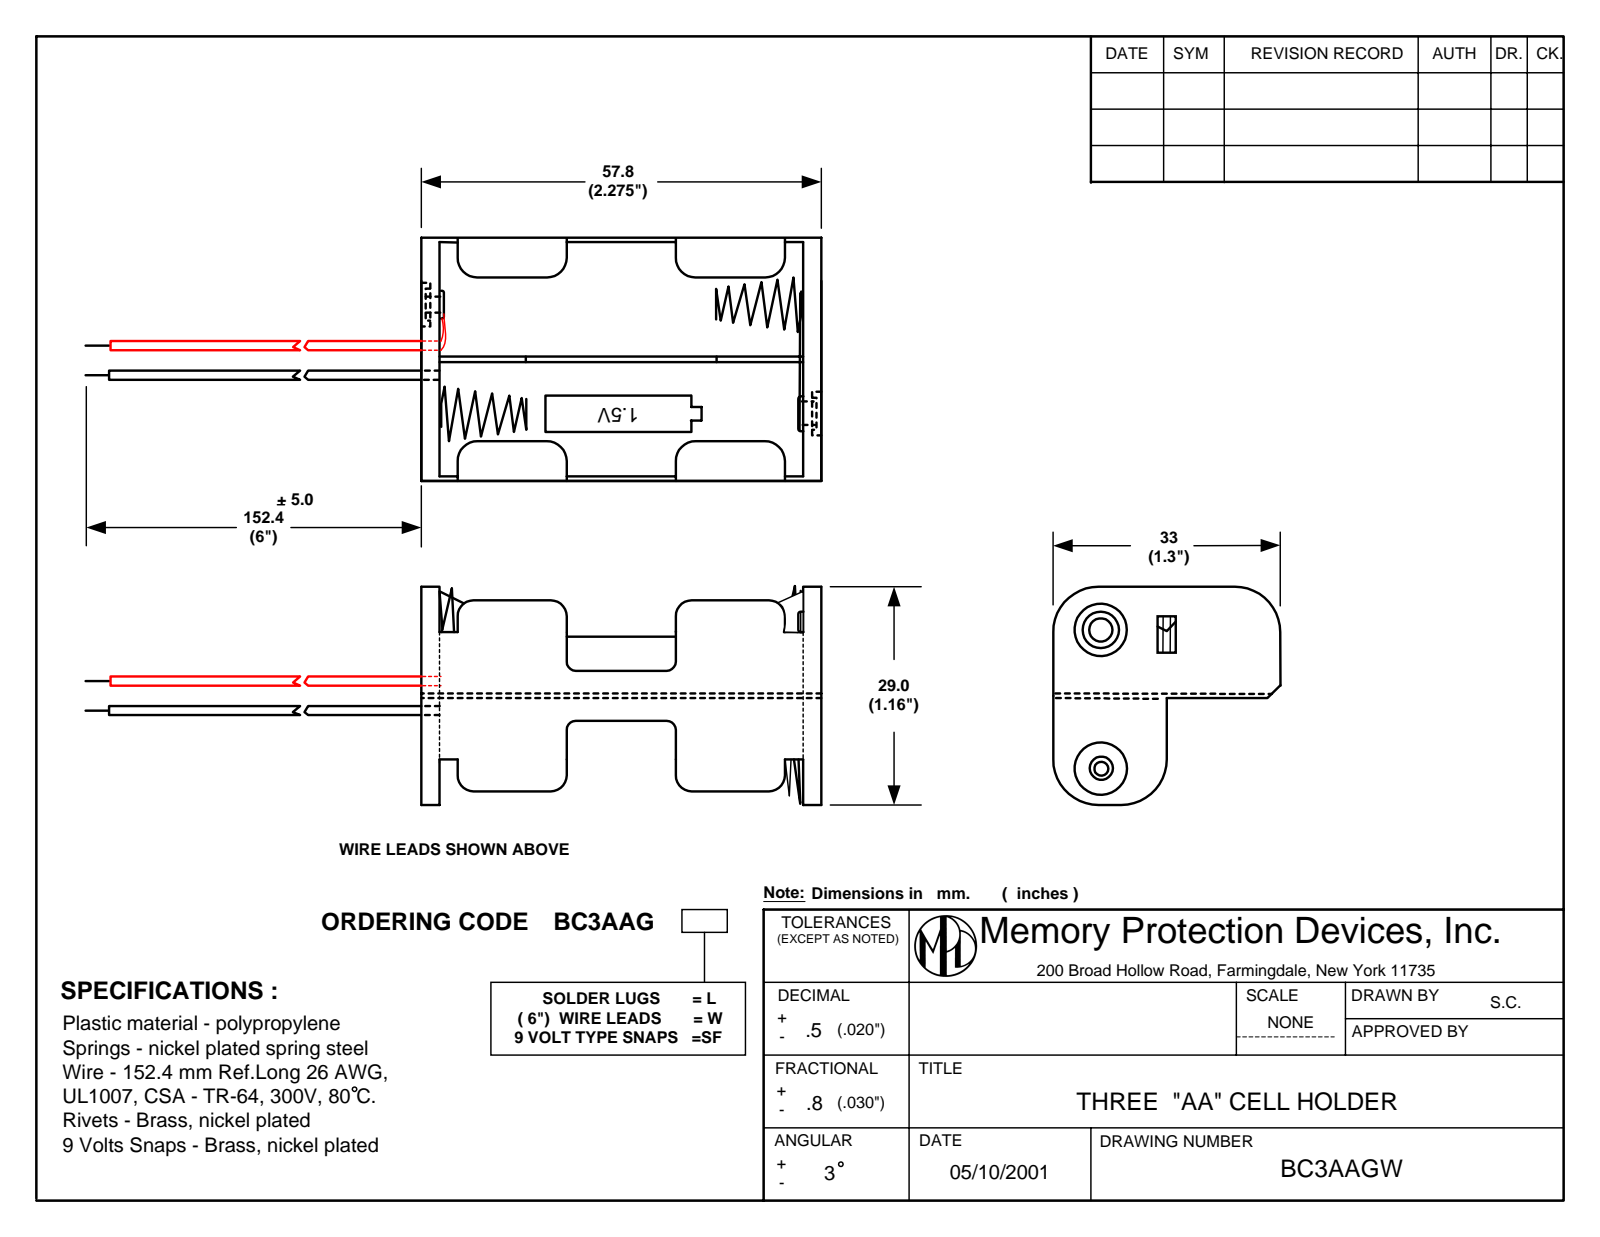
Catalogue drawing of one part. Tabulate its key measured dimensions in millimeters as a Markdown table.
| quantity | value |
| --- | --- |
| part name | BC3AAGW |
| STEP written by | SolidWorks 2016 (AUTOMOTIVE_DESIGN) |
| units | millimeters |
| bodies | 12 solids, 404 faces (186 planar, 148 cylindrical, 70 other) |
| overall size | 210.2 × 33 × 29 |
| volume | 8 665 mm³ |
| surface area | 14 486 mm² |
| round holes (diameter × count) | 2 × 4, 2.3 × 3, 3 × 3, 7.6 × 3, 0.4 × 2, 1.93 × 1 |
| round bosses / shafts (diameter × count) | 6.2 × 3, 3.5 × 3, 0.6 × 3, 0.81 × 2, 5 × 1, 0.7 × 1 |
| partial cylindrical surfaces (radius × count) | 2.5 × 16, 5 × 4, 5.22 × 4, 5.53 × 4 |
| main face-to-face distances | 1.1, 1.55, 15.95, 56.7, 0.55, 16.5, 15.4, 17.05, 14.85, 3.1 |
| hole center spacings | 6.37, 7.07, 8.3, 11.96, 12.54, 13.26, 16.5, 17.1 |
